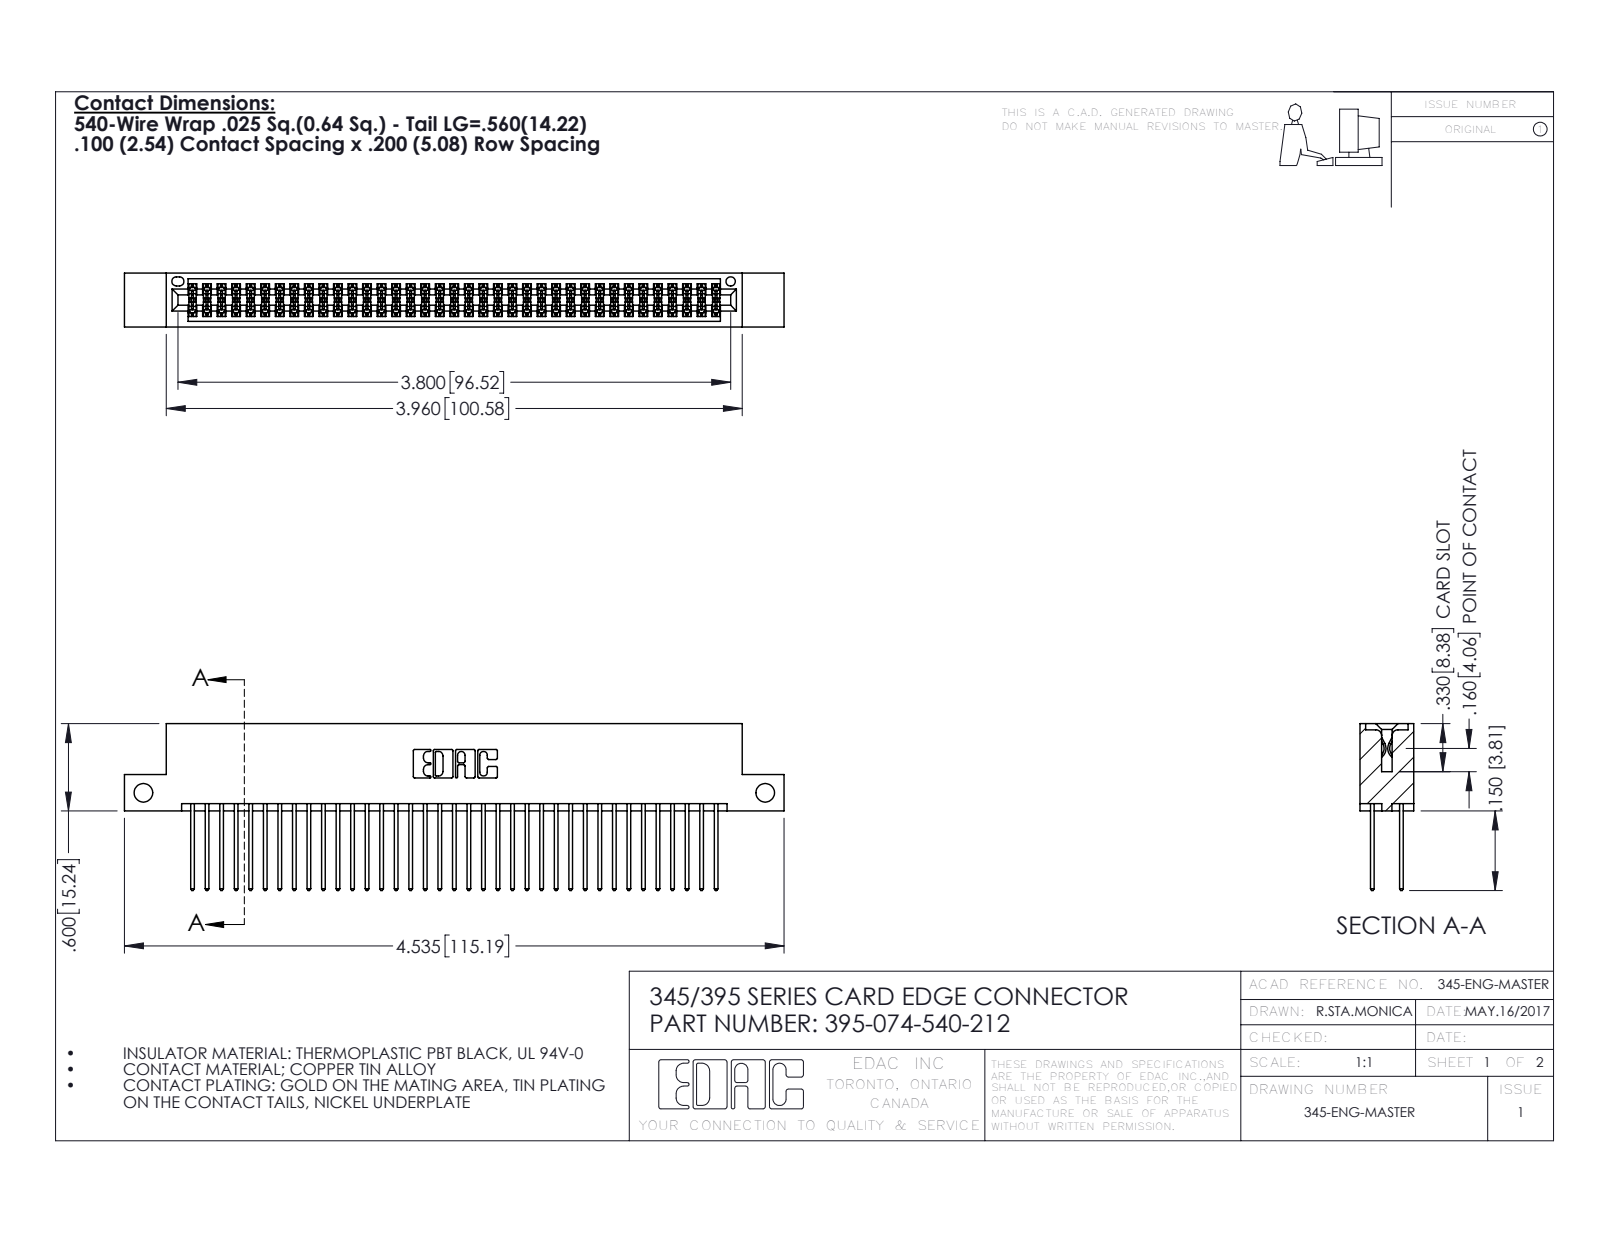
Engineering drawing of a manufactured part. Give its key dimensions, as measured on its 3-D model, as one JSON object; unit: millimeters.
{"part_name": "395-074-540-212; 345 Part_Flush Mounting Lugs - Side Mount; 345-292-001_345-293-140", "step_written_by": "SolidWorks 2016 (CONFIG_CONTROL_DESIGN)", "units": "millimeters", "bodies": {"solids": 75, "faces": 3826, "planar": 2522, "cylindrical": 1304, "other": 0}, "overall_size": [115.2, 29.1, 9.4], "volume_mm3": 11300, "surface_area_mm2": 17830, "round_holes": [[3.3, 2], [1.6, 1]], "partial_cylinders_radius": [[0.2, 111], [0.3, 74], [0.3, 22], [0.2, 6], [0.8, 6], [0.7, 3], [0.4, 2], [0.5, 2]], "face_to_face_distances": [7.6, 1.8, 5.1, 2.5, 6.9, 0.6, 9.4, 5.7, 4.4, 3.8], "hole_center_spacings": [108.6]}
